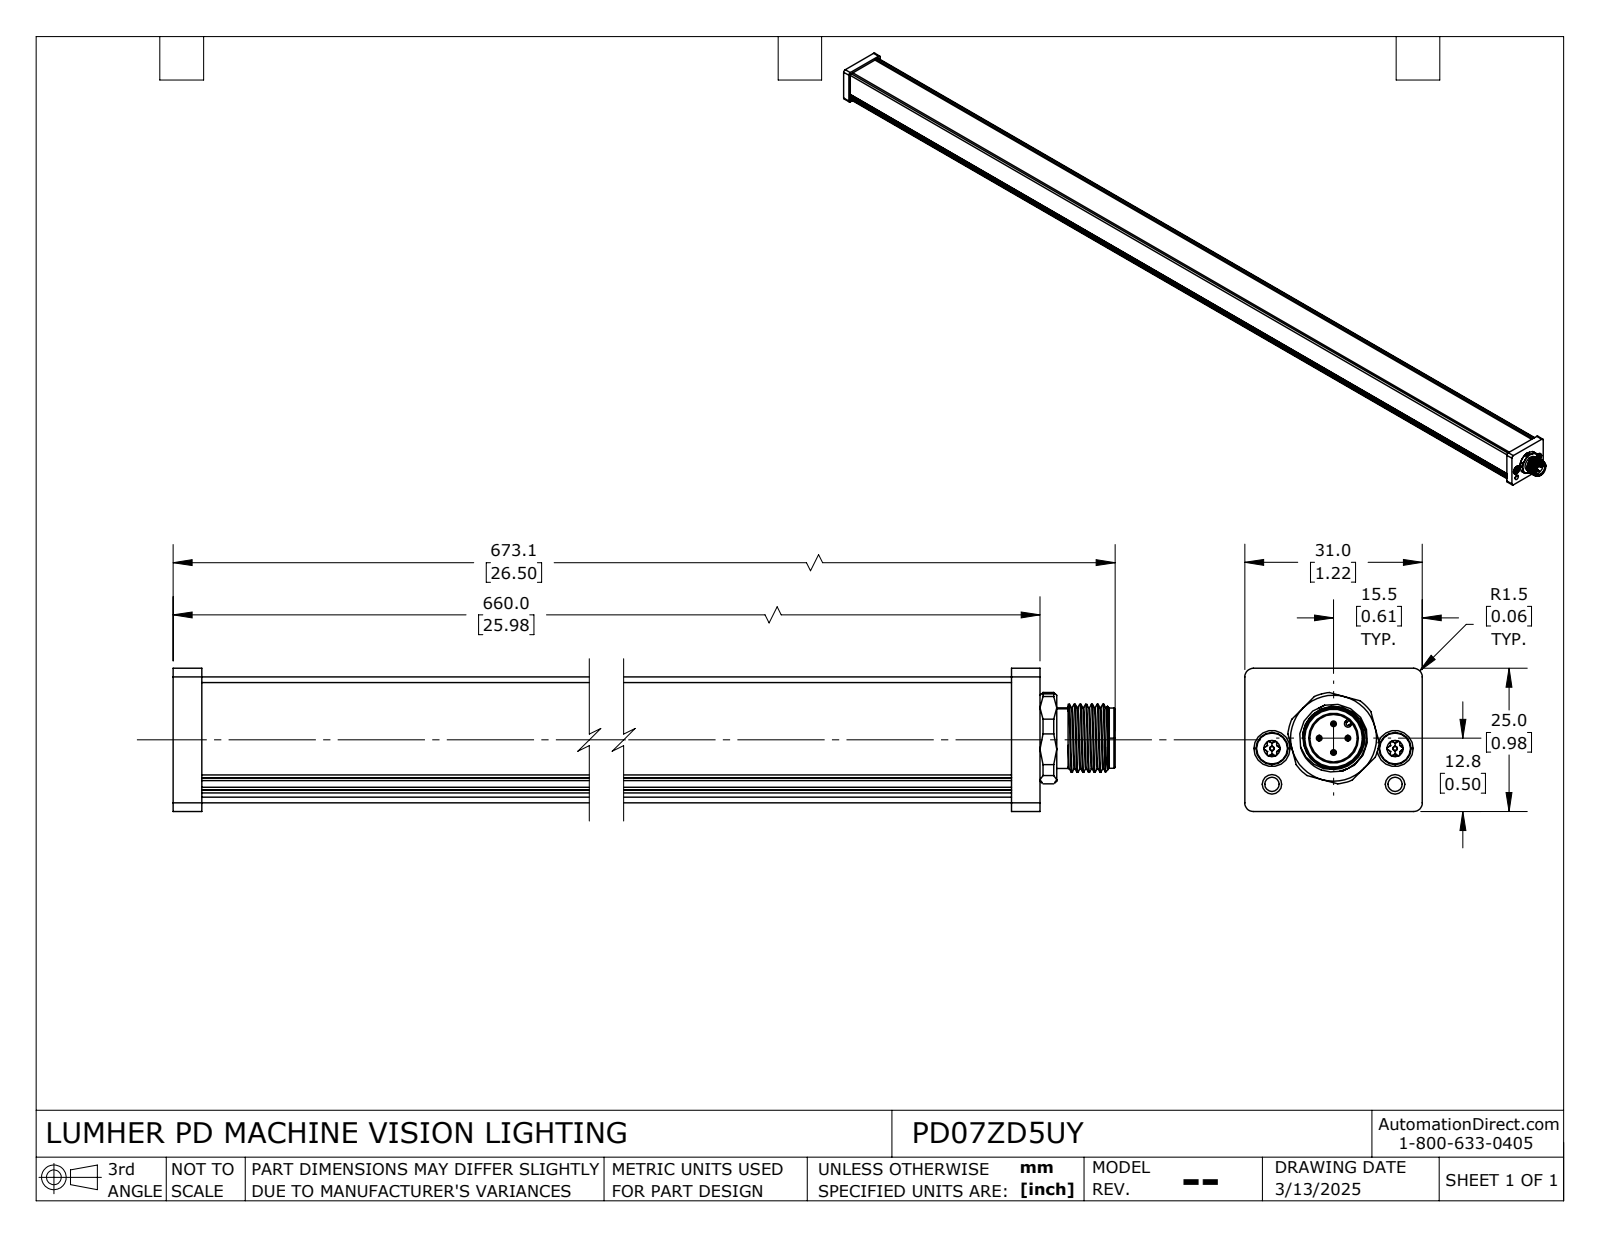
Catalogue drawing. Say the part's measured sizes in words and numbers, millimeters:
The part is named "PD07__5_Y". Its 3-D file was written by "SolidWorks 2024 (AUTOMOTIVE_DESIGN)". It is 1 solid with 563 faces: 89 planar, 296 cylindrical and 178 other. Overall it measures 673.1 by 31 by 25 millimeters. Its volume is 389 571 cubic millimeters and its surface area 85 558 square millimeters. Round holes: 4 of diameter 1.45, 4 of diameter 3.4, 2 of diameter 2.5, 1 of diameter 8.3, 1 of diameter 9.4. Round bosses or shafts: 4 of diameter 1.4, 4 of diameter 1, 2 of diameter 5.6, 2 of diameter 3, 2 of diameter 0.8, 1 of diameter 11.9, 1 of diameter 10.6, 1 of diameter 10.5. Partial cylindrical surfaces (rounded edges, fillets, slot ends): 24 of radius 0.57, 12 of radius 0.25, 8 of radius 0.5, 8 of radius 1, 6 of radius 3, 4 of radius 1.5, 2 of radius 0.3, 2 of radius 1.02. The main face-to-face distances are 28, 1, 1.5, 22, 21.75, 27, 2.5, 2, 3, 25.5. The hole center spacings are 2.5, 3.54, 5, 6.25, 8.44, 10.77, 10.9, 11.53.
